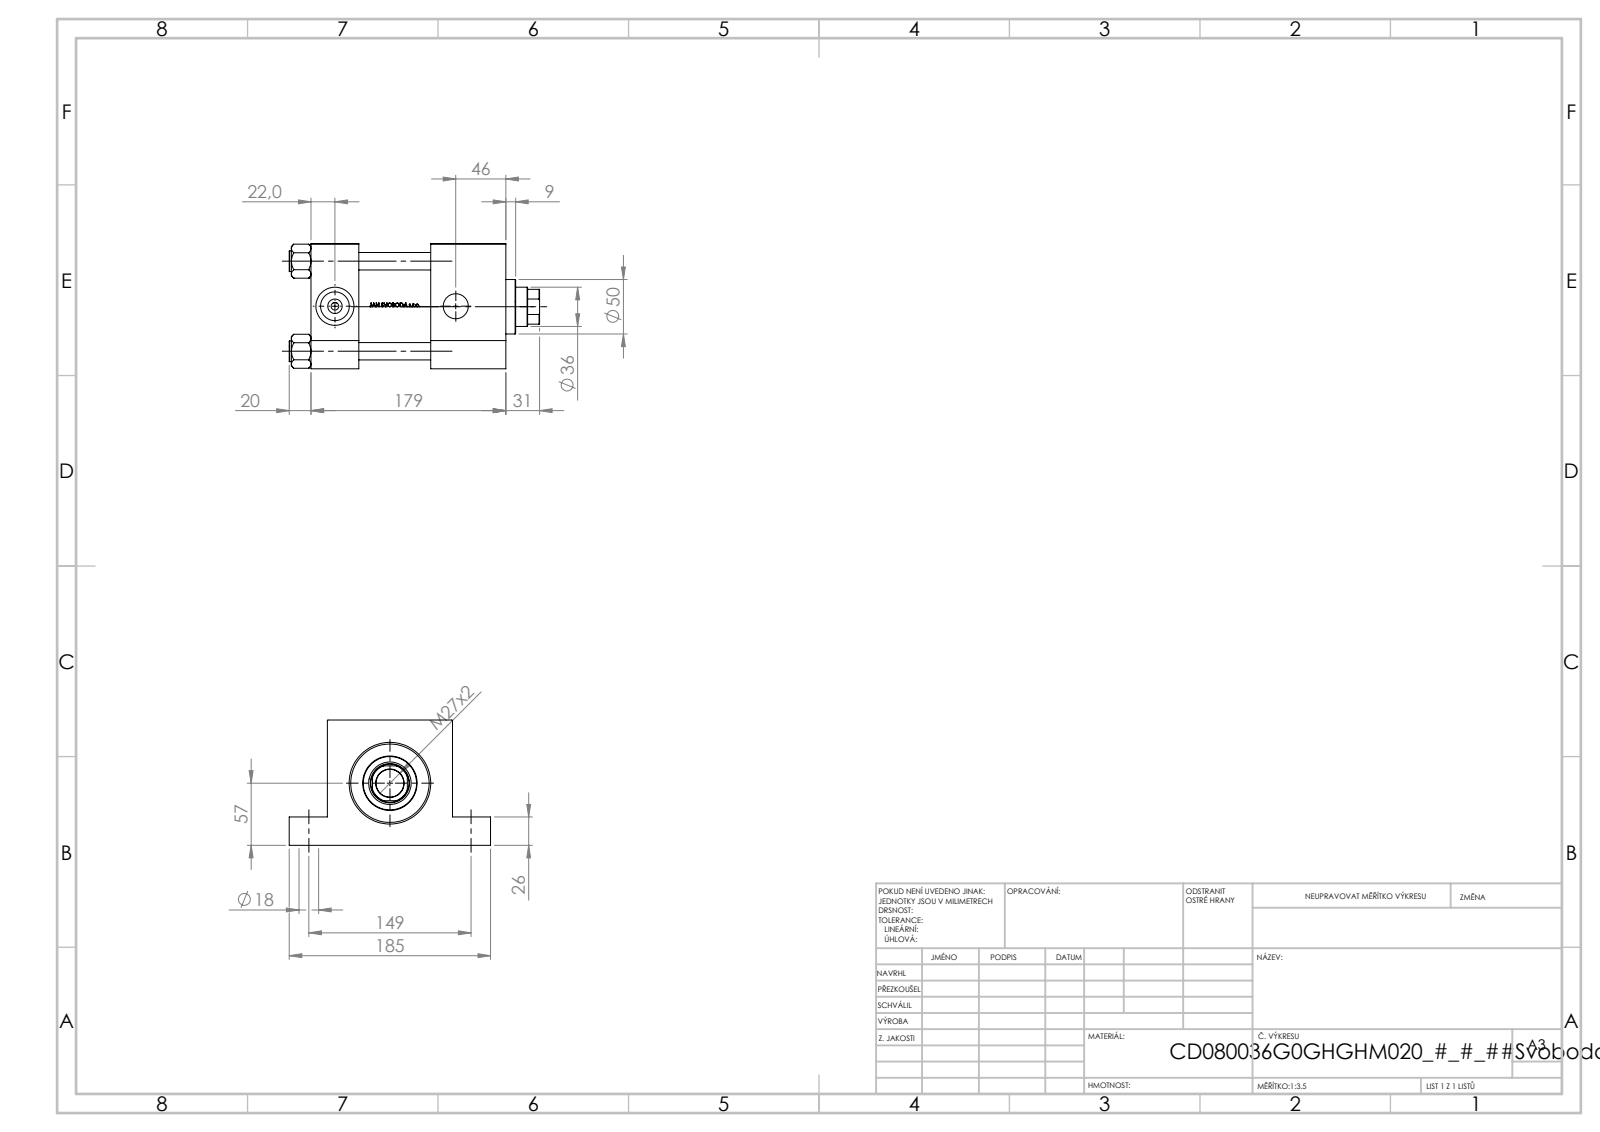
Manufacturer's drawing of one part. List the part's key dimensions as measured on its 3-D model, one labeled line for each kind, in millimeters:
Part name (STEP PRODUCT): V215CD_G_TYCINKA; V215CD_NUT_M5_G; V215CD_VCP_G; V215CD_VC_G (+1 more)
STEP written by: SolidWorks 2019 (CONFIG_CONTROL_DESIGN)
Units: millimetres
Bodies: 11 solids, 1135 faces (479 planar, 124 cylindrical, 532 other)
Overall size (bounding box): 230 × 185 × 115
Volume: 1 990 000 mm³ · Surface area: 289 607 mm²
Round holes (diameter × count): ⌀16 ×4, ⌀18 ×4, ⌀7 ×2, ⌀26.44 ×2, ⌀23 ×1, ⌀25.5 ×1, ⌀35 ×1, ⌀36 ×1, ⌀39 ×1, ⌀61 ×1, ⌀72 ×1, ⌀80 ×1
Round bosses / shafts (diameter × count): ⌀19 ×4, ⌀86 ×1, ⌀50 ×1
Partial cylindrical surfaces — rounded edges, fillets, slot ends (radius × count): R17.5 ×1
Main face-to-face distances: 115, 44, 179, 135, 110, 89, 66, 69, 26, 35
Hole centre spacings: 82.7, 58.13, 58.83, 116.96, 125, 149, 194.49, 111
